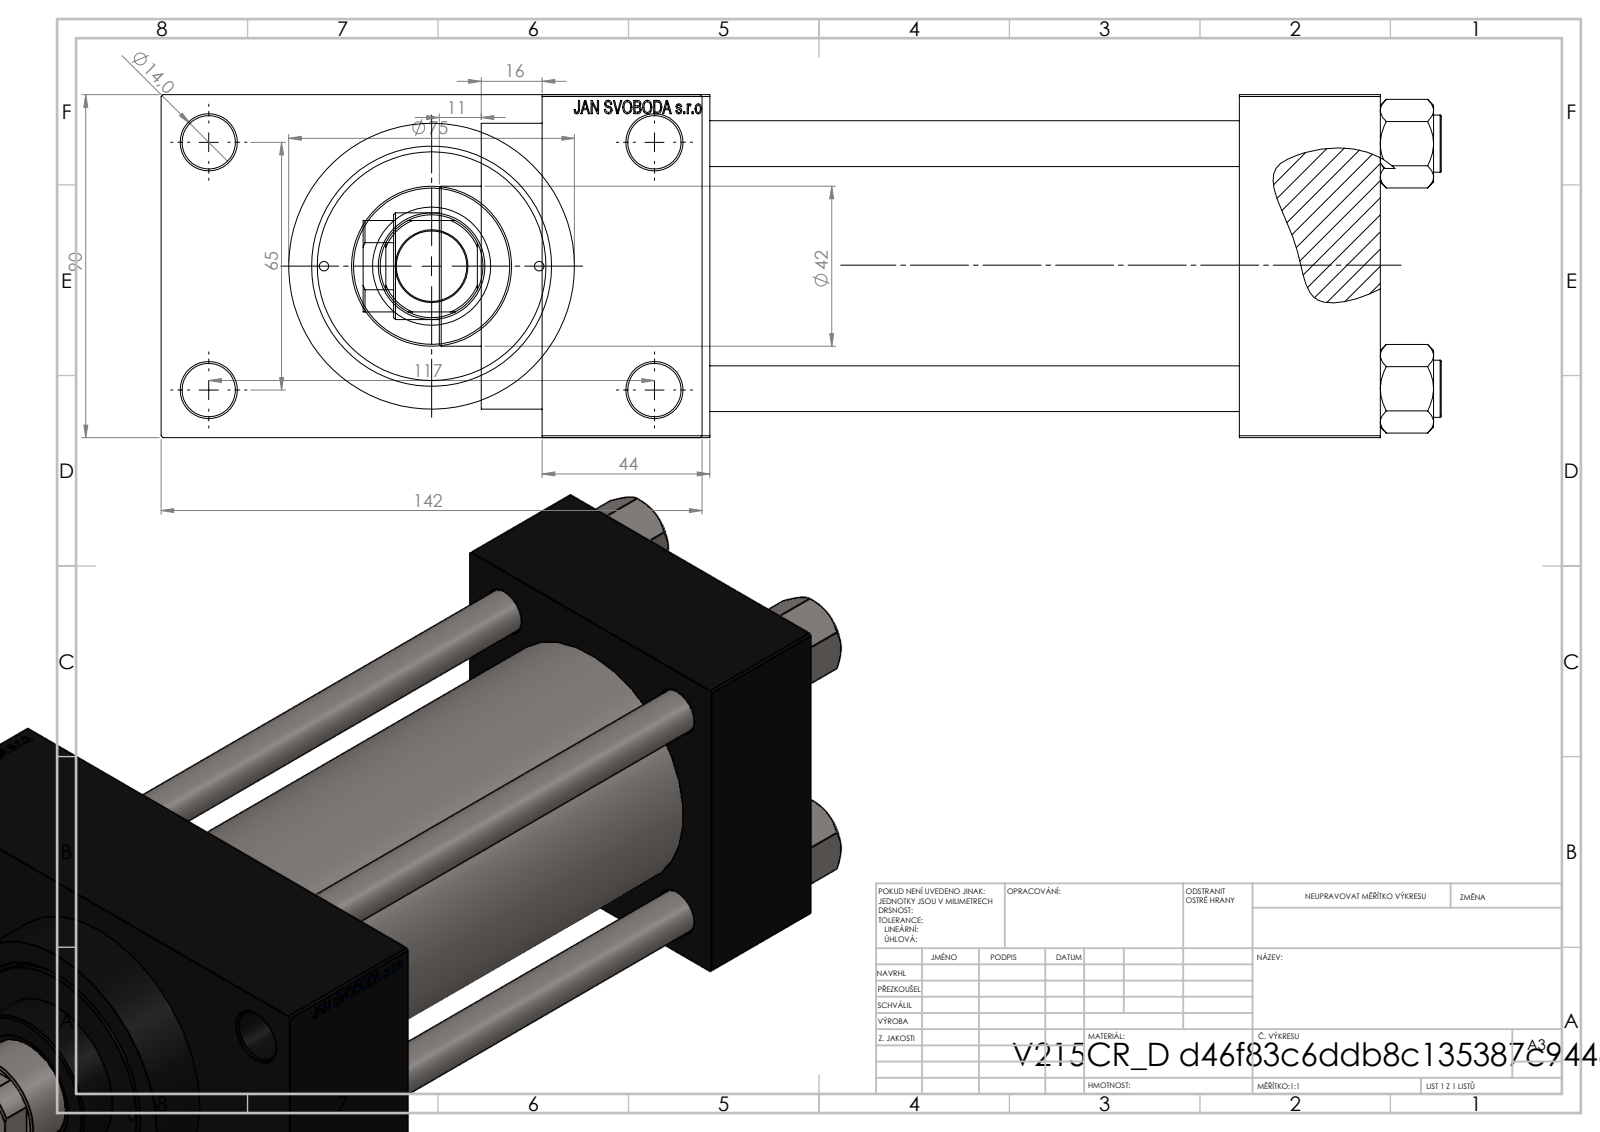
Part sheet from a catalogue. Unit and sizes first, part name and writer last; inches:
Units: inches
Overall size (bounding box): 11.142 × 5.591 × 3.543
Round holes (diameter × count): ⌀0.472 ×4, ⌀0.551 ×4, ⌀0.098 ×2, ⌀0.276 ×2, ⌀0.825 ×2, ⌀1.181 ×2, ⌀0.728 ×1, ⌀1.102 ×1, ⌀1.22 ×1, ⌀1.969 ×1, ⌀2.362 ×1, ⌀2.48 ×1
Round bosses / shafts (diameter × count): ⌀0.591 ×4, ⌀2.953 ×1, ⌀2.717 ×1, ⌀1.654 ×1
Partial cylindrical surfaces — rounded edges, fillets, slot ends (radius × count): R0.531 ×1
Main face-to-face distances: 3.543, 5.472, 1.457, 6.929, 7.205, 8.661, 1.732, 1.024, 4.567, 0.63
Hole centre spacings: 1.037, 1.275, 1.748, 1.79, 2.531, 2.635, 2.694, 2.748
Volume: 75.12 in³ · Surface area: 391.4 in²
Bodies: 11 solids, 1111 faces (499 planar, 92 cylindrical, 520 other)
Part name (STEP PRODUCT): V215_VC_A; V215CR_D_Body; V215CR_VCP_D; V215CR_D_TYCINKA (+1 more)
STEP written by: SolidWorks 2019 (CONFIG_CONTROL_DESIGN)
